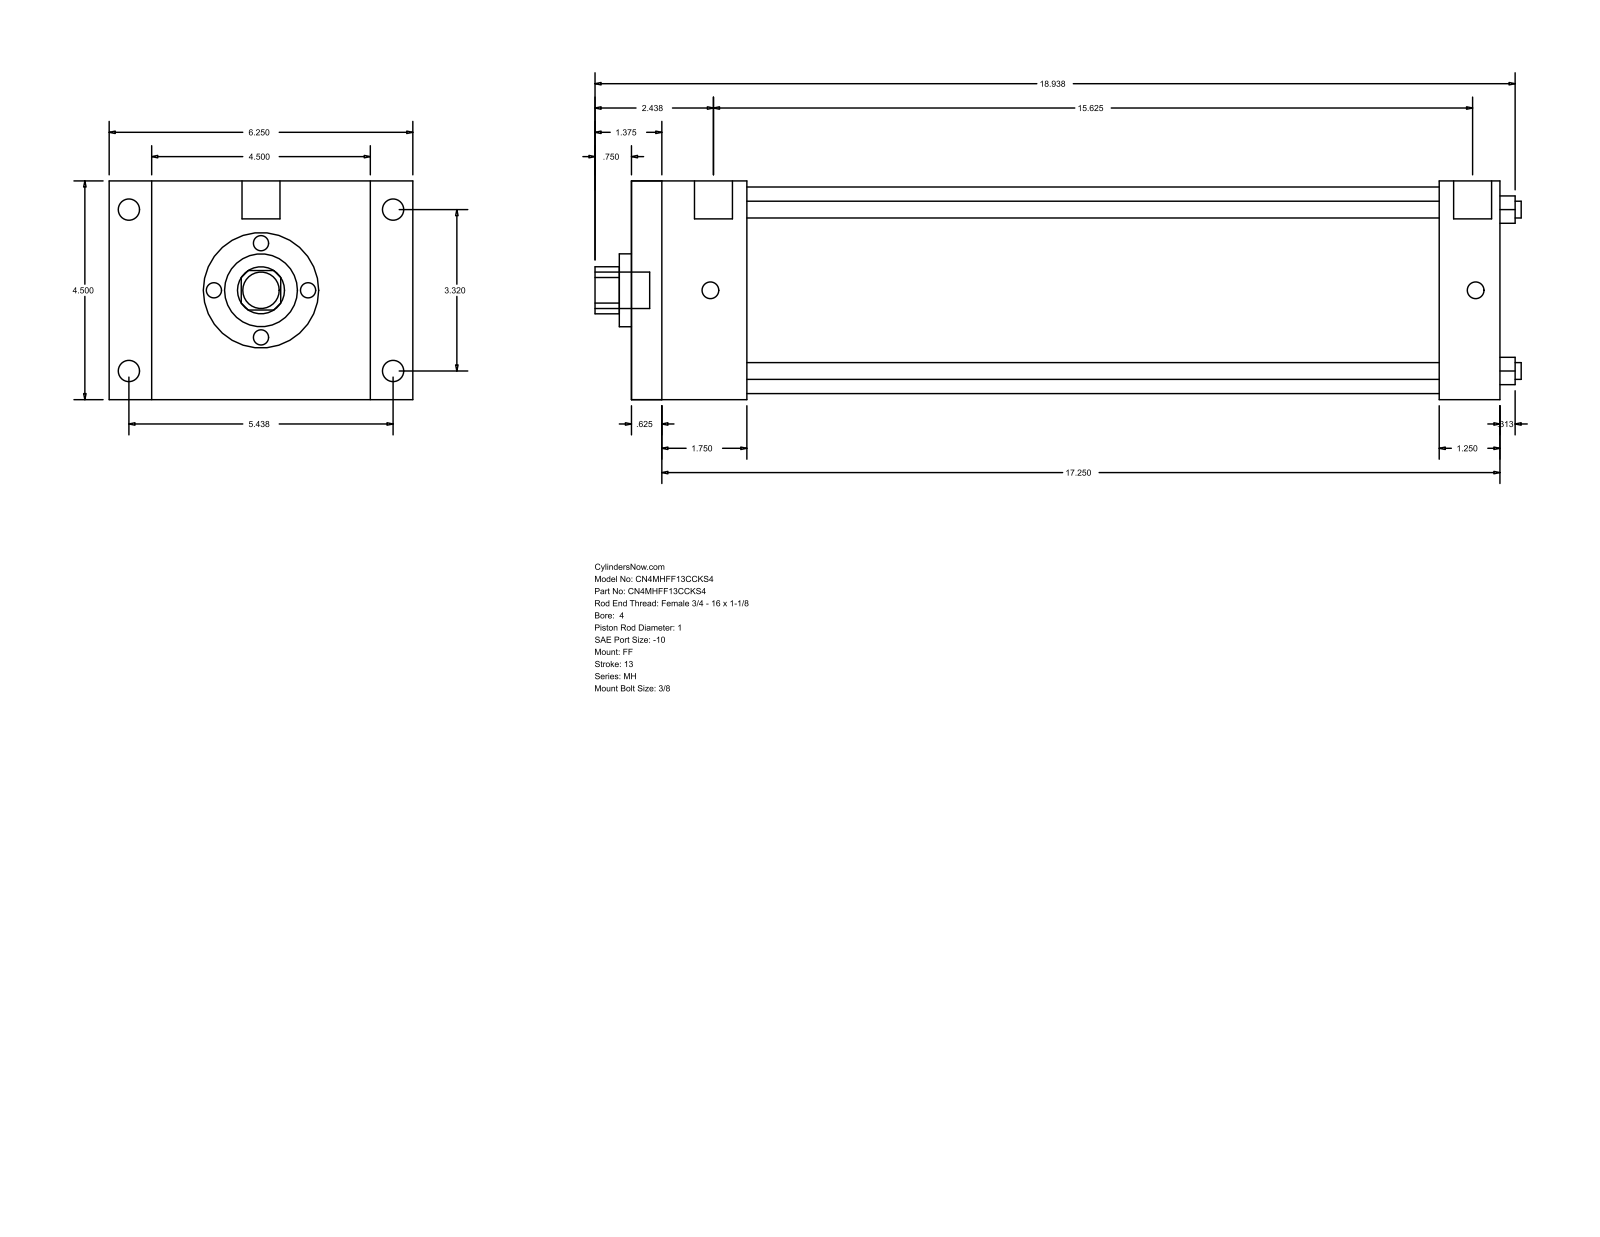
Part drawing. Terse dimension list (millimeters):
name: MH_FF__0400_1
written by: GSSL Pune (CONFIG_CONTROL_DESIGN)
unit: mm
bodies: 0 solids, 92 faces (64 planar, 28 cylindrical, 0 other)
size: 484.19 × 158.75 × 114.3
holes: 4× ⌀8.76, 1× ⌀25.4, 1× ⌀38.1, 1× ⌀107.95
bosses: 4× ⌀11.13, 4× ⌀8.73, 2× ⌀19.84, 1× ⌀19.05
rounds: 1× R12.29
face distances: 114.3, 454.02, 15.87, 438.15, 60.33, 44.46, 393.69, 422.27, 406.4, 361.94
hole spacings: 59.62, 84.32, 119.25
